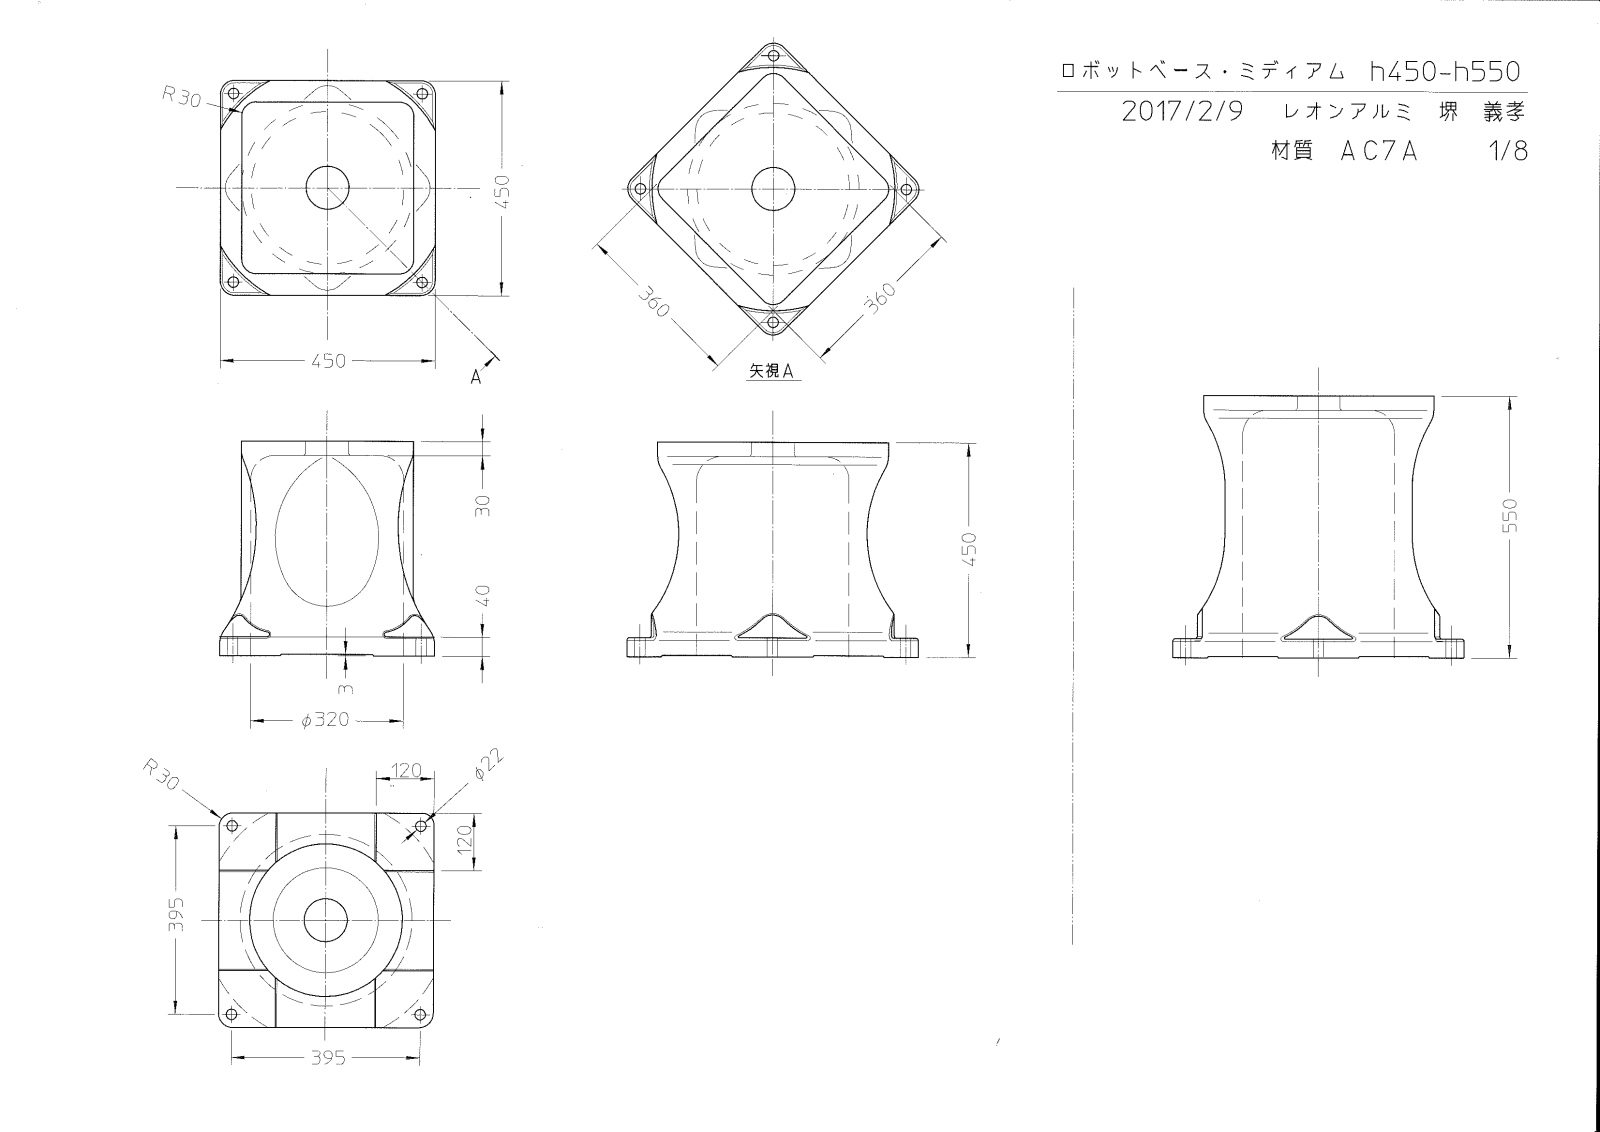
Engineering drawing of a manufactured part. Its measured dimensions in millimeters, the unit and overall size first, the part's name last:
Units: millimetres
Overall size (bounding box): 1250 × 550 × 450
Round holes (diameter × count): ⌀22 ×8, ⌀90 ×2, ⌀320 ×2
Partial cylindrical surfaces — rounded edges, fillets, slot ends (radius × count): R30 ×16, R50 ×8, R5 ×4, R380 ×4, R180 ×2, R255 ×2
Main face-to-face distances: 450, 550, 100, 405, 45, 420, 513.33, 30, 93.33, 130
Hole centre spacings: 279.31, 395, 800, 558.61, 634.04, 892.2, 1016.86, 405
Volume: 53 480 000 mm³ · Surface area: 2 971 000 mm²
Bodies: 2 solids, 244 faces (30 planar, 68 cylindrical, 146 other)
Part name (STEP PRODUCT): パーツ14
STEP written by: Spatial InterOp 3D (CONFIG_CONTROL_DESIGN)
